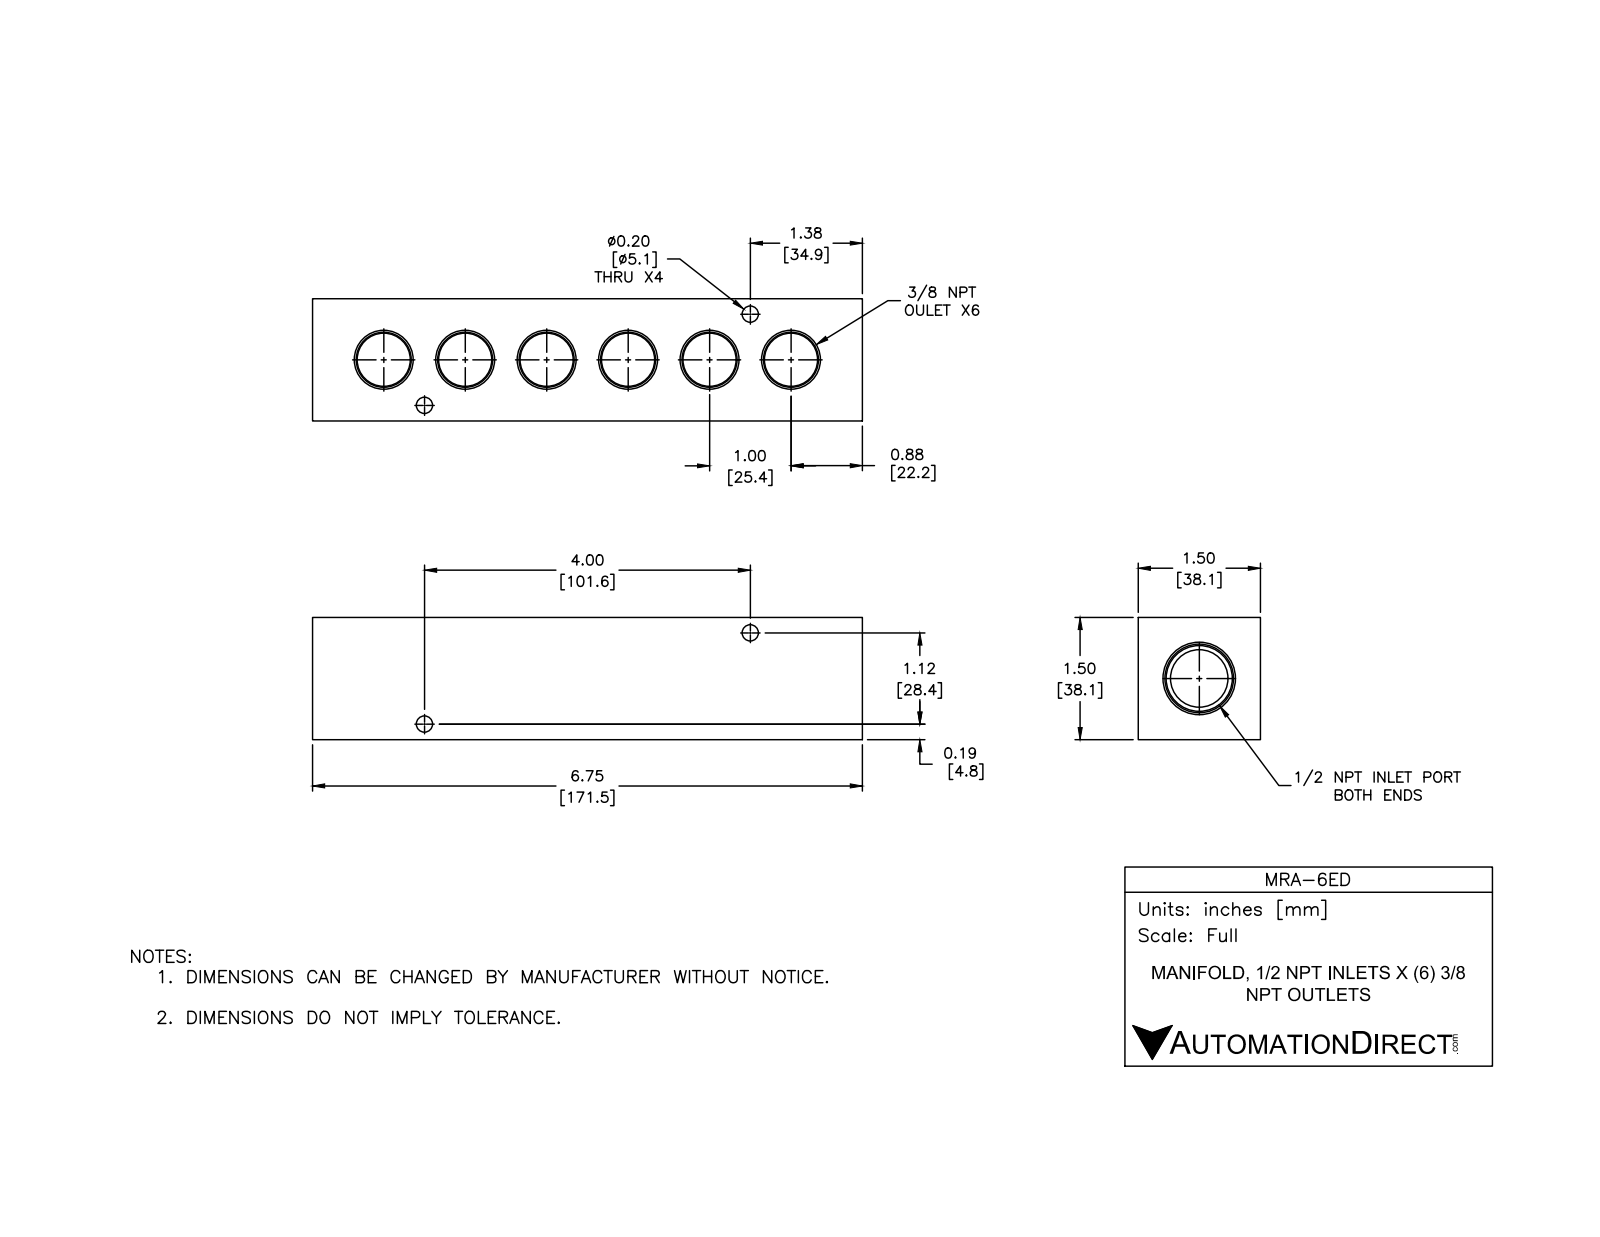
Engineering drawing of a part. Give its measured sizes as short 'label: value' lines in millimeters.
name: MRA-6ED
written by: SolidWorks 2015 (CONFIG_CONTROL_DESIGN)
unit: mm
bodies: 1 solid, 82 faces (20 planar, 30 cylindrical, 32 other)
size: 171.5 × 38.1 × 38.1
volume: 186 000 mm³; area: 41 700 mm²
holes: 6× ⌀14.3, 4× ⌀5.1, 1× ⌀17.9
face distances: 38.1, 171.5, 27.7, 10.4, 13.5, 158, 144.5
hole spacings: 25.4, 19.1, 50.8, 76.2, 40.7, 65.1, 90, 101.6
